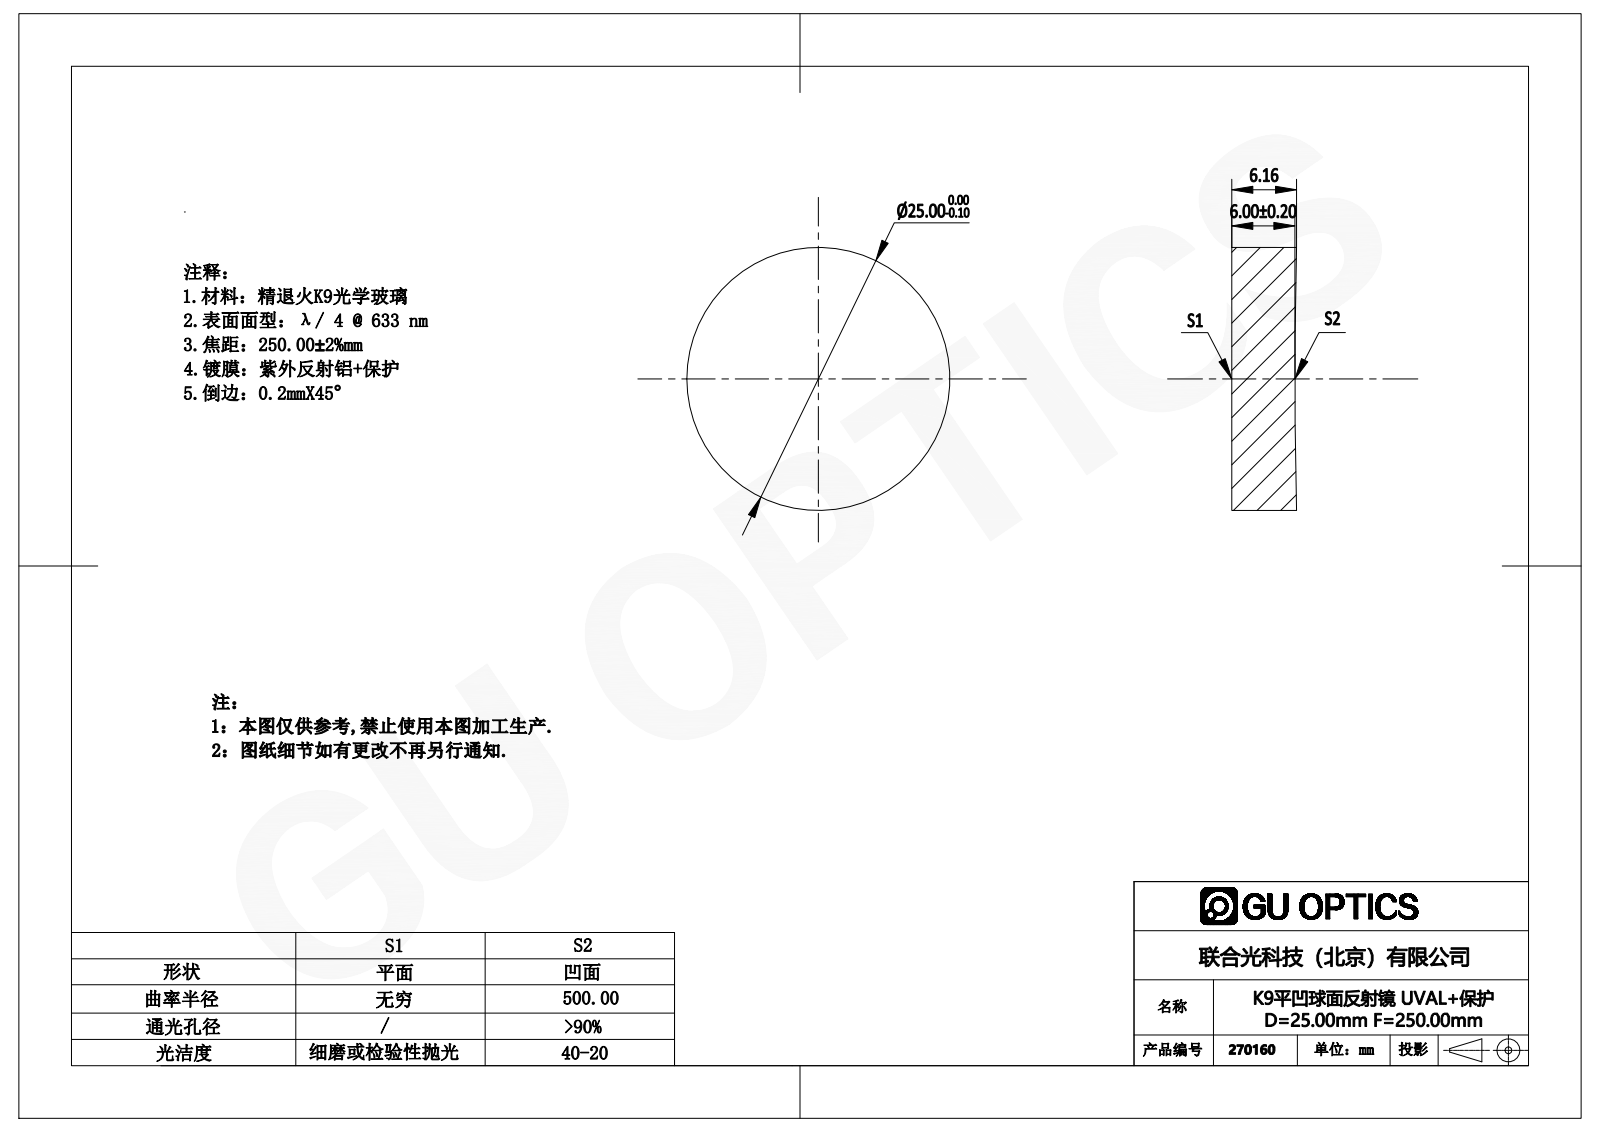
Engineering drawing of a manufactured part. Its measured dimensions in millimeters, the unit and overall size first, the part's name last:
Units: millimetres
Overall size (bounding box): 25 × 25 × 6.16
Round bosses / shafts (diameter × count): ⌀25 ×1
Volume: 2 984 mm³ · Surface area: 1 465 mm²
Bodies: 1 solid, 5 faces (1 planar, 2 cylindrical, 2 other)
Part name (STEP PRODUCT): 270030
STEP written by: SolidWorks 2016 (AUTOMOTIVE_DESIGN)
